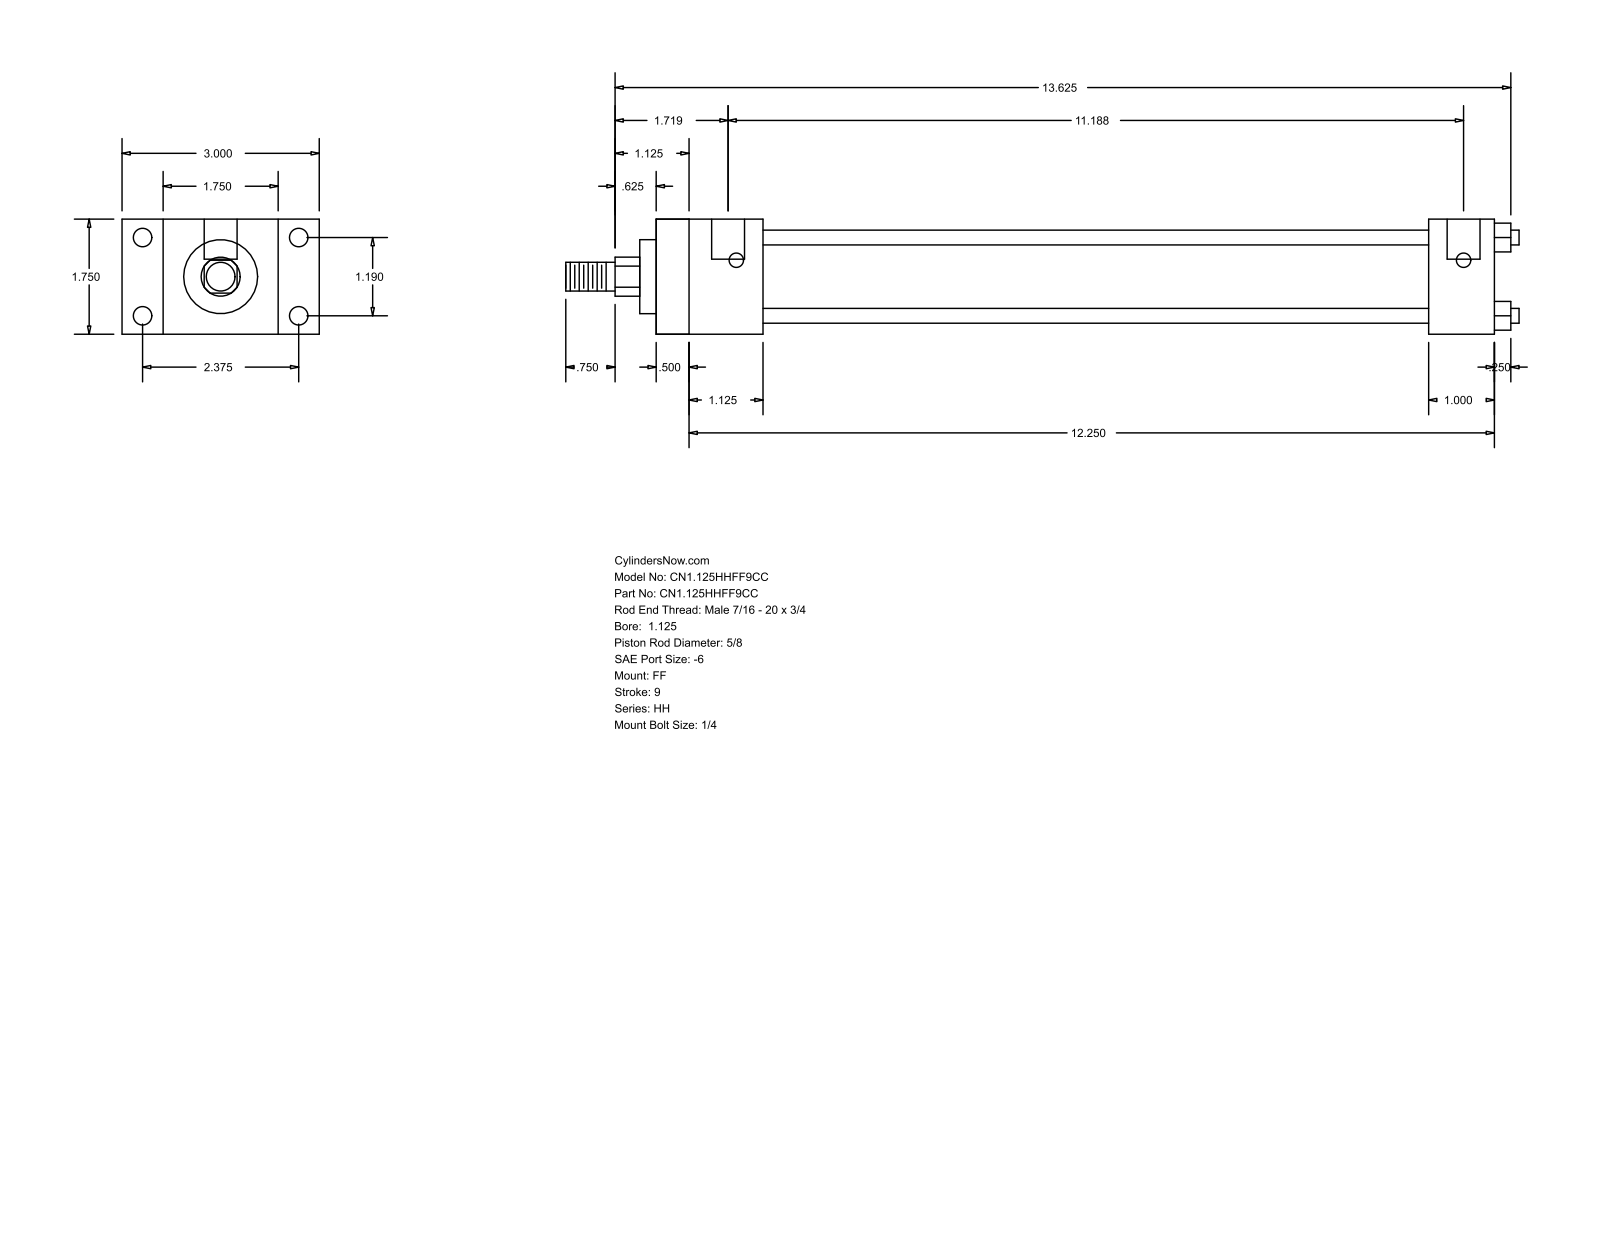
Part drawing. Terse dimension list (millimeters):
name: HH_FF__0112_0.625
written by: GSSL Pune (CONFIG_CONTROL_DESIGN)
unit: mm
bodies: 0 solids, 92 faces (64 planar, 28 cylindrical, 0 other)
size: 368.3 × 76.2 × 44.45
holes: 4× ⌀5.56, 4× ⌀7.14, 2× ⌀12.7
bosses: 4× ⌀5.71, 1× ⌀34.92, 1× ⌀28.57, 1× ⌀15.88, 1× ⌀11.11
rounds: 1× R7.54
face distances: 44.46, 323.85, 12.69, 311.16, 15.87, 28.58, 60.33, 41.27, 298.44, 285.75
hole spacings: 30.22, 60.32, 67.47, 280.99, 3.17, 284.16
